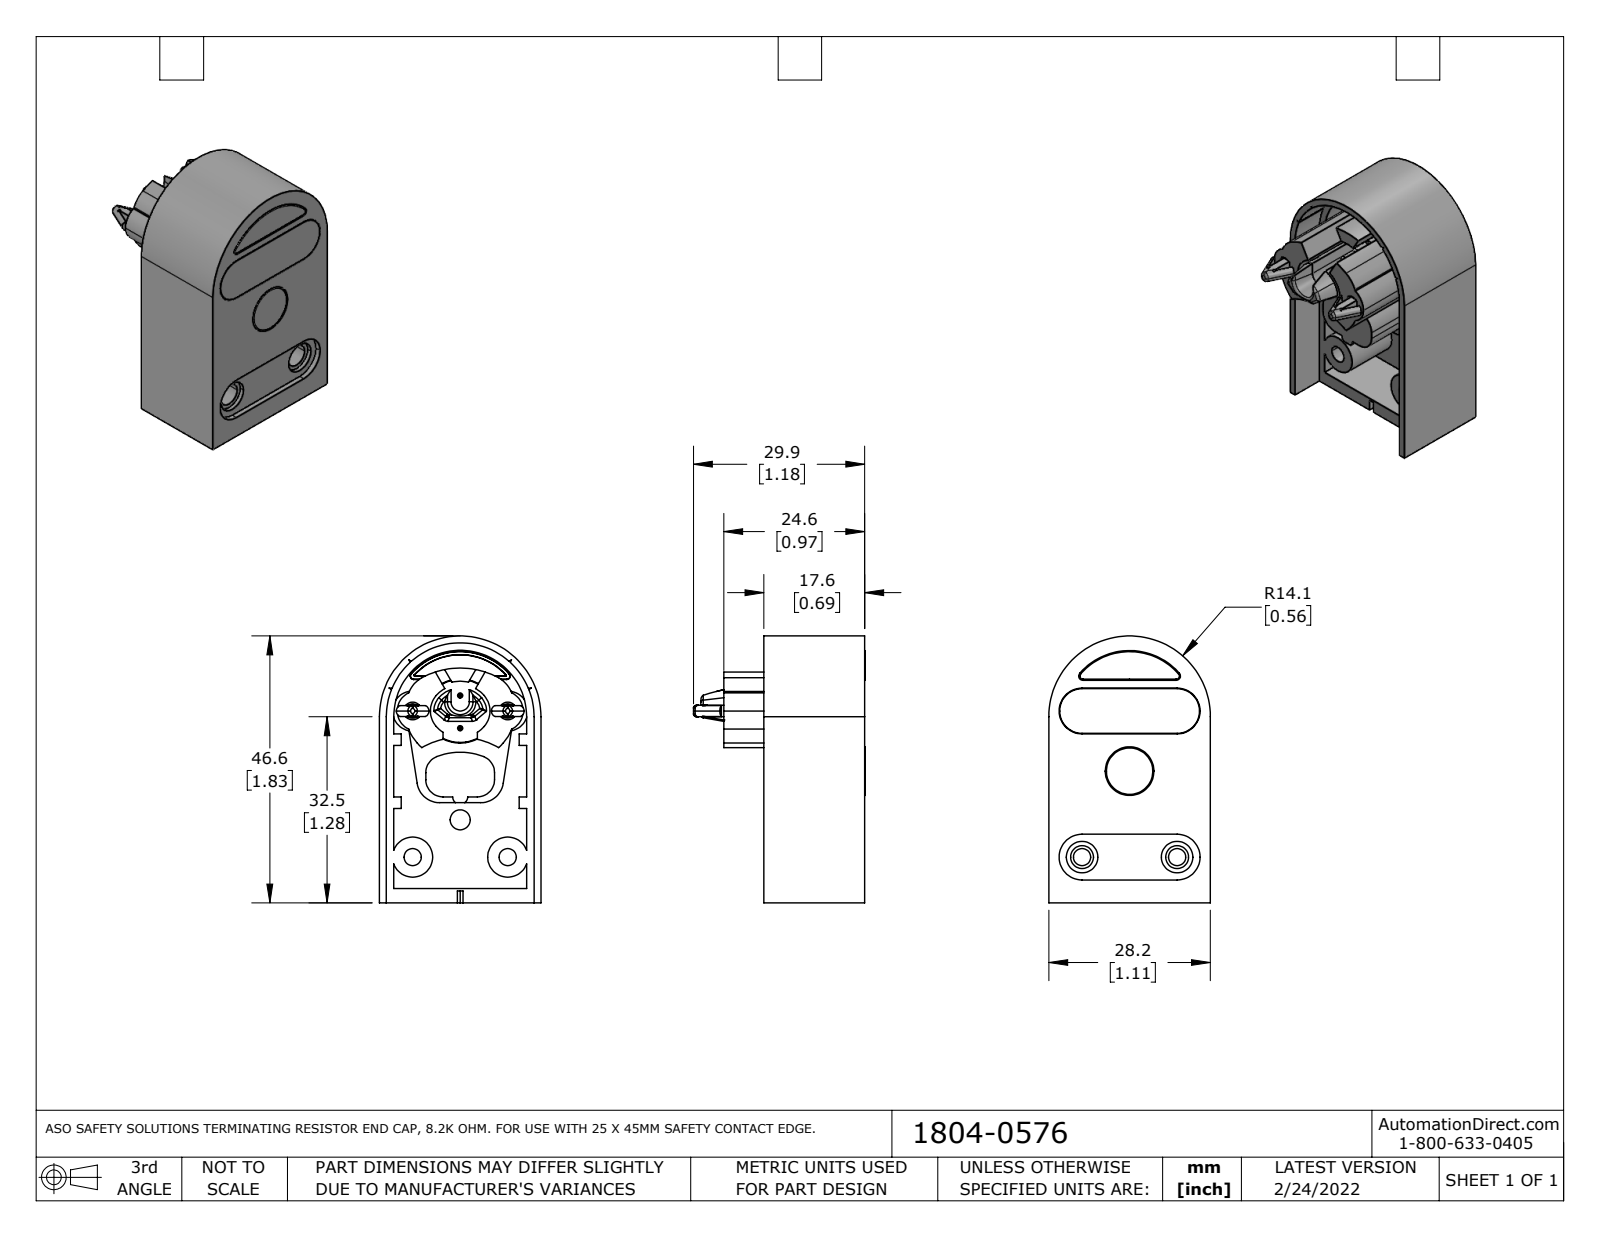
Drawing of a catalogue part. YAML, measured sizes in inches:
part_name: "1804-0576_Default"
step_written_by: "SolidWorks 2021 (CONFIG_CONTROL_DESIGN)"
units: inches
bodies: {solids: 6, faces: 506, planar: 184, cylindrical: 222, other: 100}
overall_size: [1.835, 1.181, 1.11]
volume: 0.717
surface_area: 20.14
round_holes:
  - {diameter: 0.02, count: 4}
  - {diameter: 0.157, count: 4}
  - {diameter: 0.217, count: 4}
  - {diameter: 0.138, count: 3}
  - {diameter: 0.028, count: 2}
  - {diameter: 0.118, count: 2}
  - {diameter: 0.122, count: 2}
  - {diameter: 0.031, count: 1}
round_bosses_or_shafts:
  - {diameter: 0.276, count: 2}
  - {diameter: 0.197, count: 2}
  - {diameter: 0.138, count: 2}
  - {diameter: 0.098, count: 2}
  - {diameter: 0.079, count: 2}
  - {diameter: 0.065, count: 2}
  - {diameter: 0.035, count: 2}
  - {diameter: 0.024, count: 2}
partial_cylinders:
  - {radius: 0.039, count: 14}
  - {radius: 0.004, count: 9}
  - {radius: 0.012, count: 6}
  - {radius: 0.118, count: 6}
  - {radius: 0.138, count: 6}
  - {radius: 0.157, count: 6}
  - {radius: 0.02, count: 5}
  - {radius: 0.197, count: 4}
face_to_face_distances: [0.071, 0.098, 1.11, 0.039, 0.051, 1.063, 1.012, 0.031, 0.965, 0.047]
hole_center_spacings: [0.654, 0.055, 0.344, 0.348, 0.415, 0.816, 0.872, 0.892]
